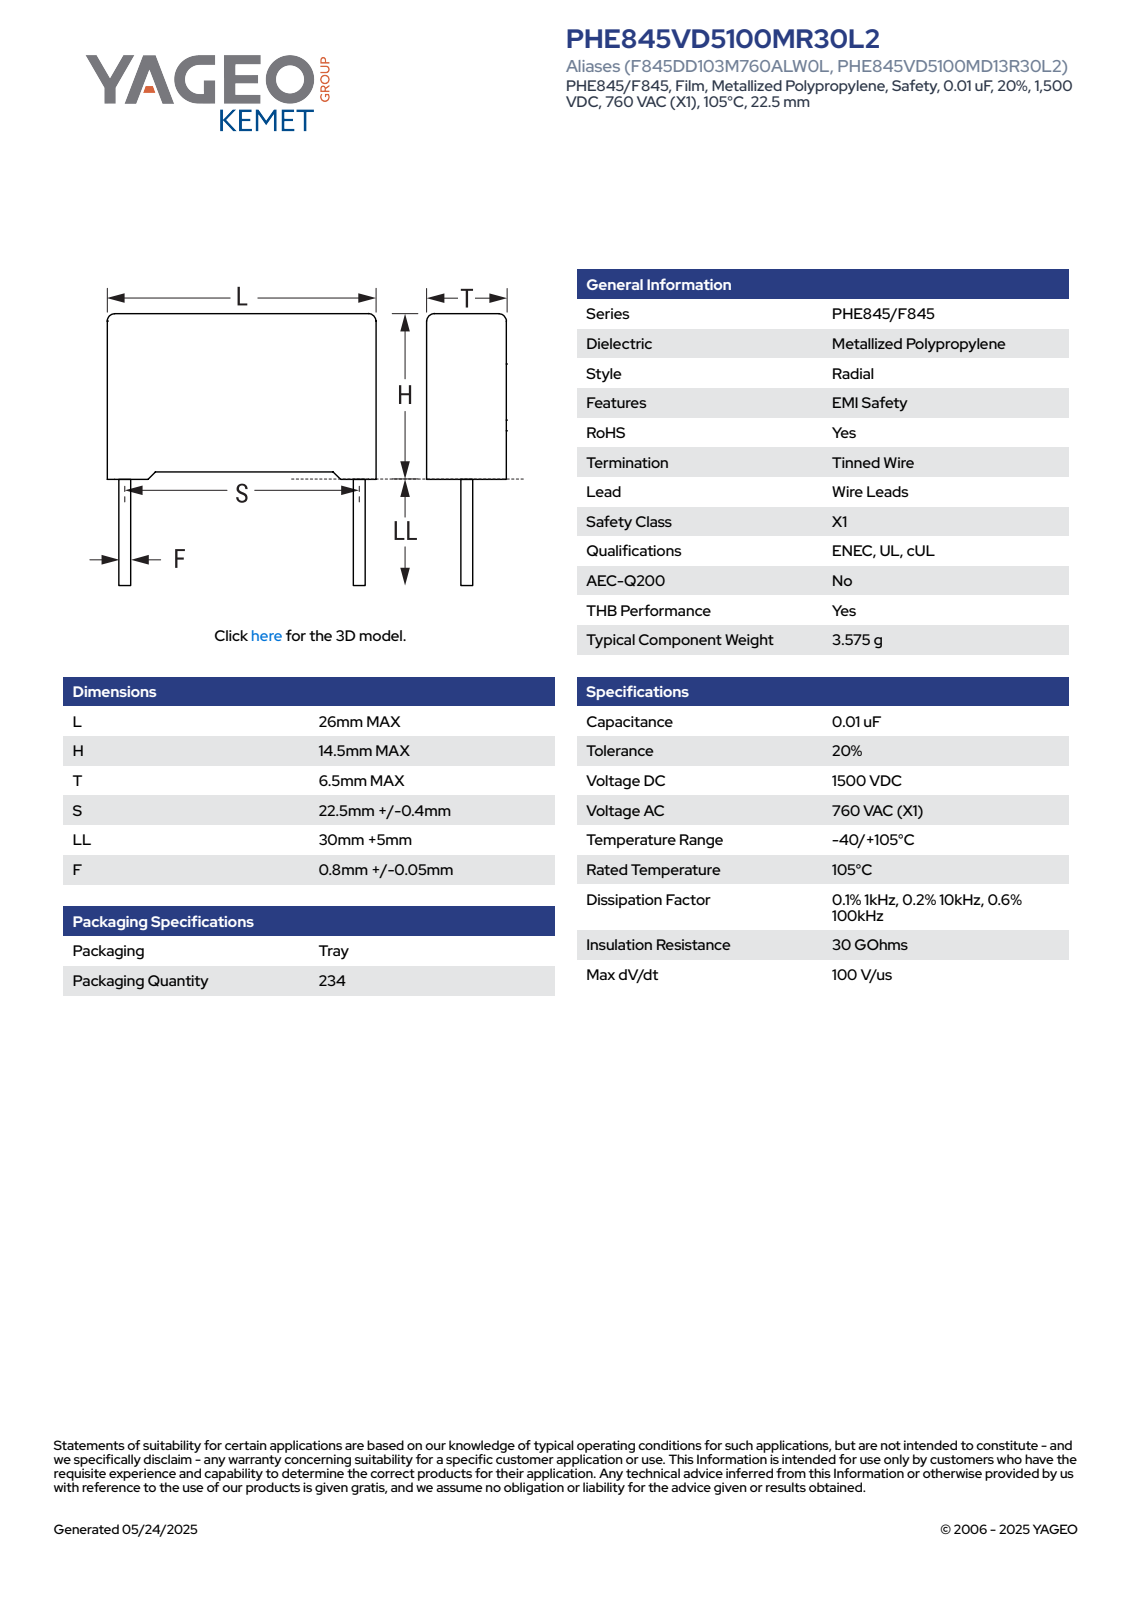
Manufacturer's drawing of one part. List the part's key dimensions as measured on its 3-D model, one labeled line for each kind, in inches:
Part name (STEP PRODUCT): CFR_RB2_26X14.5X6.5_L26H14.5T6.5S22.5LL35F0.85
STEP written by: SolidWorks 2021 (AUTOMOTIVE_DESIGN)
Units: inches
Bodies: 4 solids, 85 faces (77 planar, 8 cylindrical, 0 other)
Overall size (bounding box): 1.949 × 1.024 × 0.256
Volume: 0.146 in³ · Surface area: 2.348 in²
Round bosses / shafts (diameter × count): ⌀0.033 ×2
Partial cylindrical surfaces — rounded edges, fillets, slot ends (radius × count): R0.02 ×4
Main face-to-face distances: 0.256, 0.541, 1.024, 0.551, 0.034, 0.02, 0.03, 0.571, 0.222, 0.187
